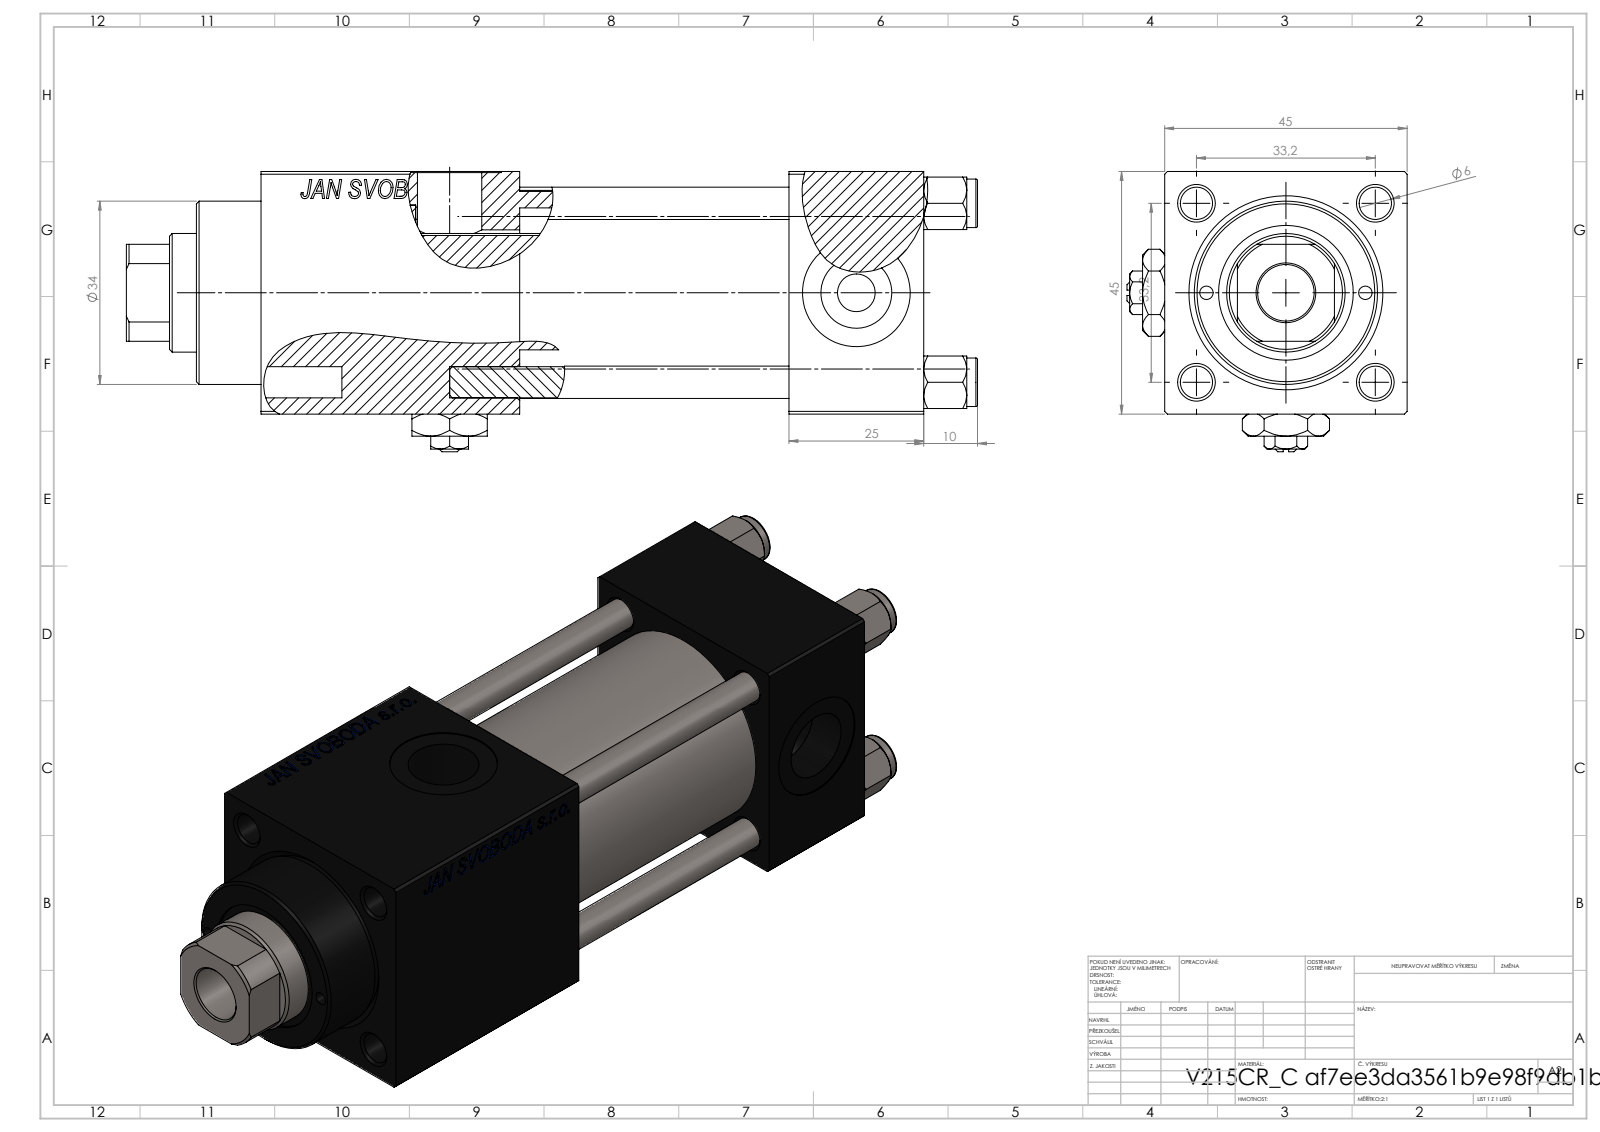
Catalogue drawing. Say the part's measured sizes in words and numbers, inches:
The part is named "Zatka_pro_OIL_PORT; V215CR_VCP_C; V215CR_C_TYCINKA; V215_VC_A (+2 more)". Its 3-D file was written by "SolidWorks 2019 (CONFIG_CONTROL_DESIGN)". It is 13 solids with 1254 faces: 574 planar, 102 cylindrical and 578 other. Overall it measures 6.22 by 2.047 by 2.047 inches. Its volume is 12.7 cubic inches and its surface area 113.8 square inches. Round holes: 4 of diameter 0.236, 2 of diameter 0.098, 2 of diameter 0.276, 2 of diameter 0.518, 2 of diameter 0.787, 1 of diameter 0.413, 1 of diameter 0.866, 1 of diameter 0.945, 1 of diameter 0.984, 1 of diameter 1.26, 1 of diameter 1.299. Round bosses or shafts: 4 of diameter 0.354, 1 of diameter 1.496, 1 of diameter 1.339. Partial cylindrical surfaces (rounded edges, fillets, slot ends): 1 of radius 0.413. The main face-to-face distances are 1.772, 0.984, 1.969, 4.843, 2.953, 3.858, 1.764, 1.89, 3.713, 2.728. The hole center spacings are 0.657, 0.924, 1.307, 1.396, 0.581, 1.848, 1.161.
